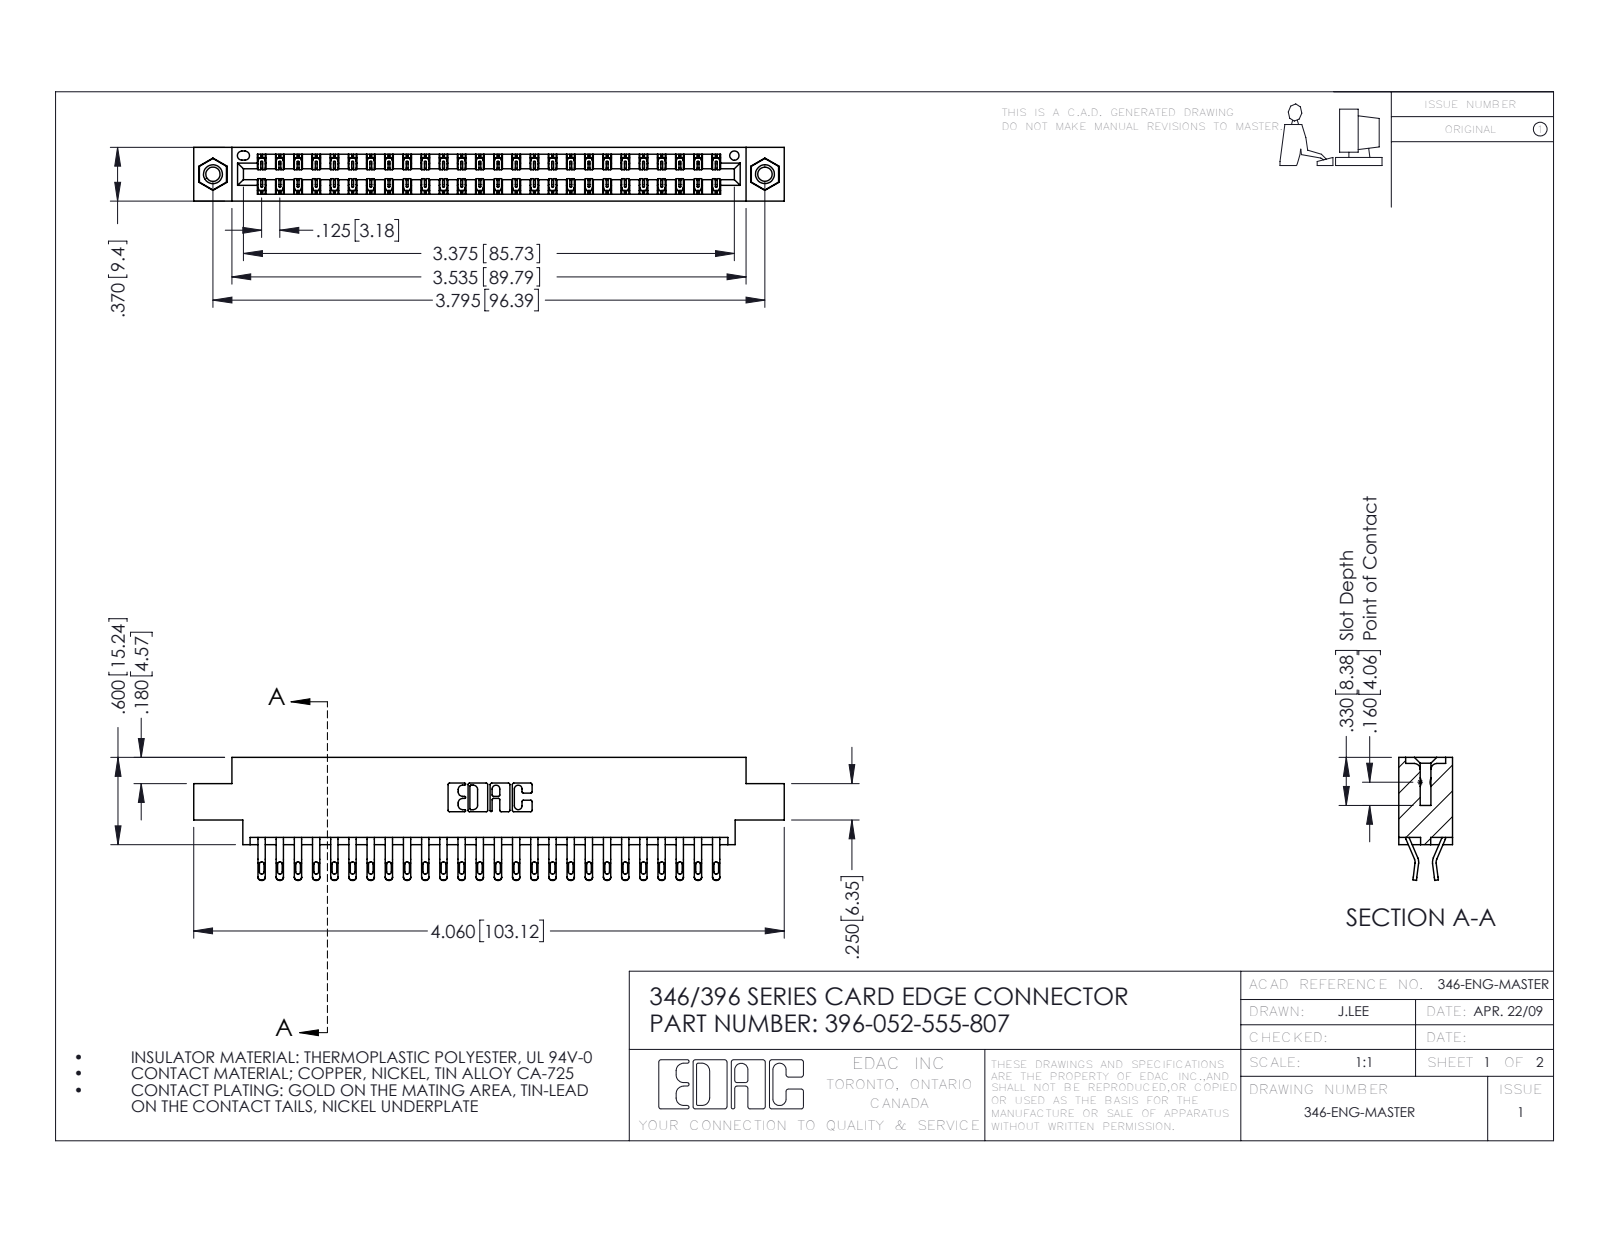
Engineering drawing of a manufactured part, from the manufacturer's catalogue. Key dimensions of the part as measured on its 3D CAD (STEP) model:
Part name (STEP PRODUCT): 345-250-001_345-250-005-103; 345-292-001_555 Tail; 396-052-555-807; 346 Part_0.170 Offset - 0.156 Dia-TI
STEP written by: SolidWorks 2016 (CONFIG_CONTROL_DESIGN)
Units: inches
Bodies: 55 solids, 3202 faces (1828 planar, 1358 cylindrical, 16 other)
Overall size (bounding box): 4.06 × 0.845 × 0.37
Volume: 0.605 in³ · Surface area: 21.9 in²
Round holes (diameter × count): ⌀0.098 ×2, ⌀0.125 ×2, ⌀0.156 ×2, ⌀0.064 ×1
Round bosses / shafts (diameter × count): ⌀0.155 ×2
Partial cylindrical surfaces — rounded edges, fillets, slot ends (radius × count): R0.016 ×104, R0.02 ×104, R0.006 ×78, R0.01 ×22, R0.007 ×6, R0.031 ×6, R0.026 ×3, R0.01 ×2
Main face-to-face distances: 0.048, 0.322, 0.37, 0.25, 0.025, 0.072, 0.298, 0.275, 0.222, 0.148
Hole centre spacings: 0.246, 3.587, 3.795
